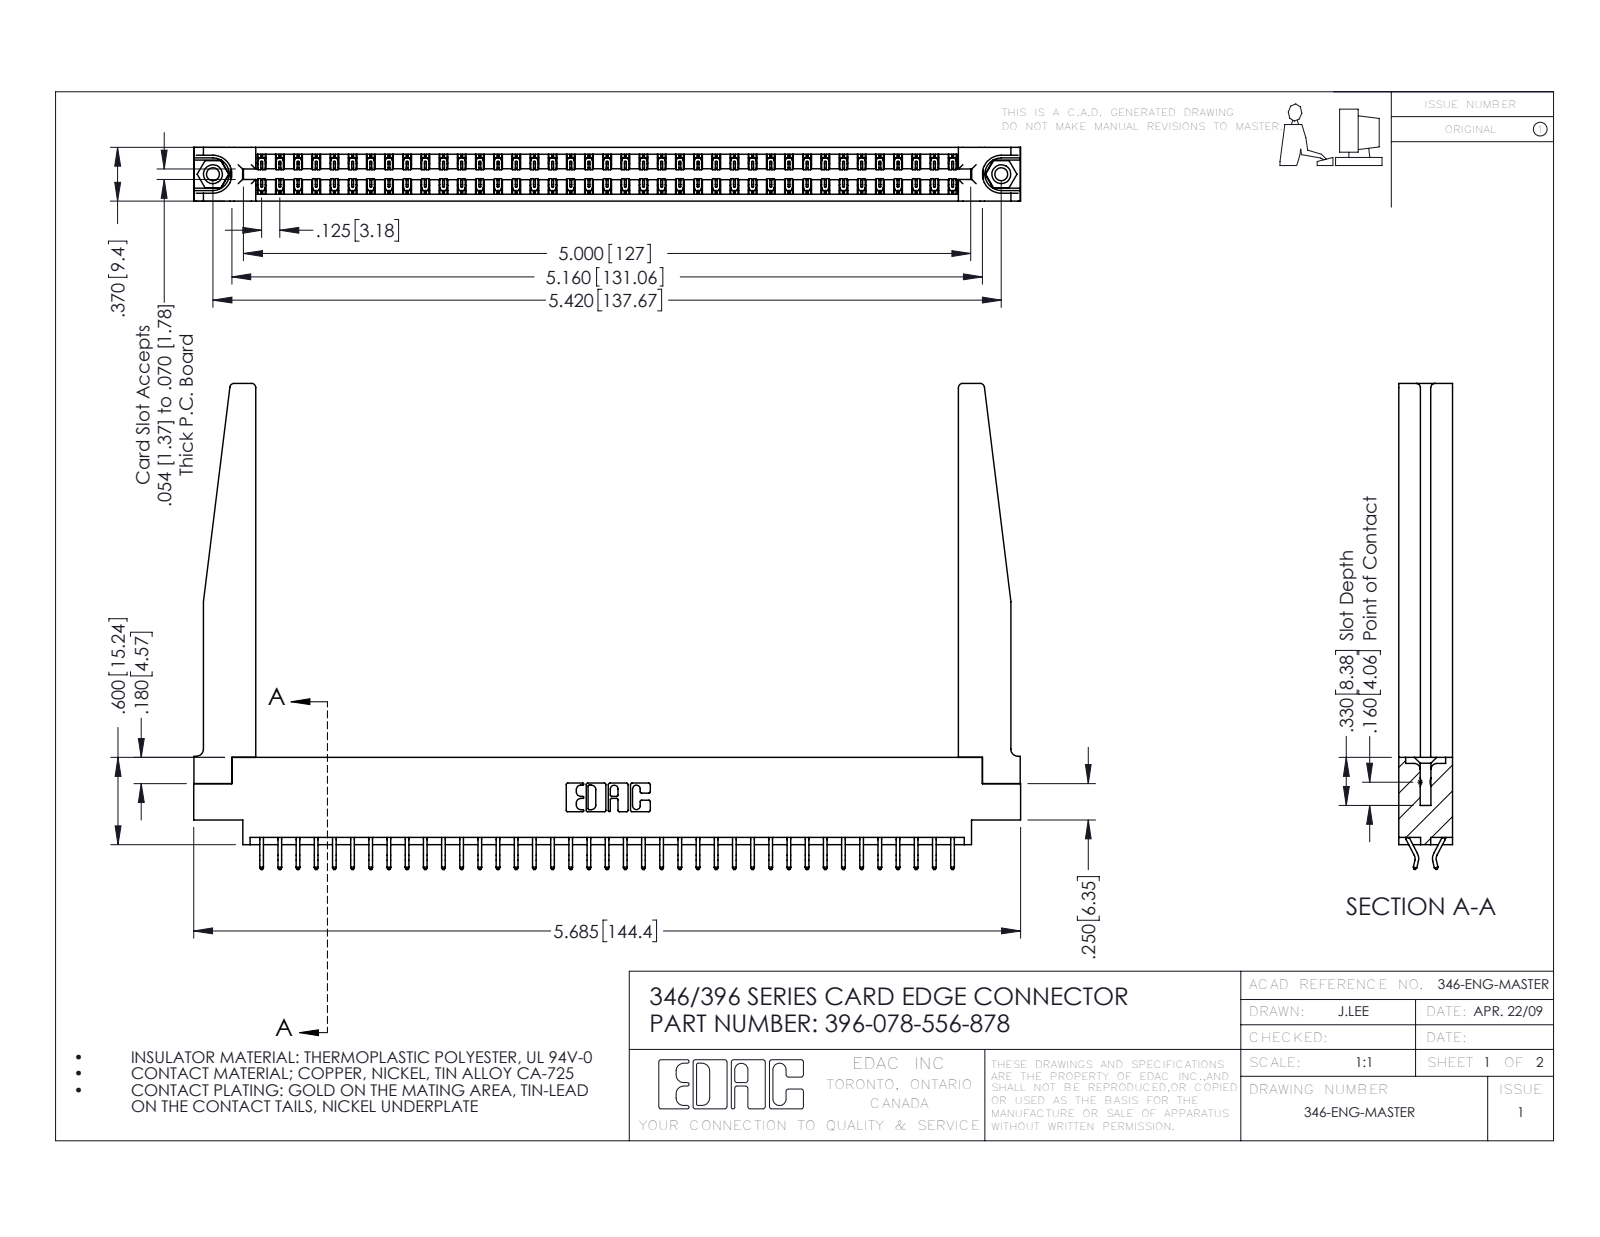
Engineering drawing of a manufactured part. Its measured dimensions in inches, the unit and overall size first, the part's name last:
Units: inches
Overall size (bounding box): 5.685 × 3.34 × 0.37
Round holes (diameter × count): ⌀0.089 ×2, ⌀0.125 ×2, ⌀0.156 ×2, ⌀0.064 ×1
Round bosses / shafts (diameter × count): ⌀0.155 ×2
Partial cylindrical surfaces — rounded edges, fillets, slot ends (radius × count): R0.006 ×117, R0.01 ×22, R0.03 ×8, R0.007 ×6, R0.031 ×6, R0.05 ×4, R0.026 ×3, R0.01 ×2
Main face-to-face distances: 0.37, 0.048, 0.322, 0.072, 0.148, 0.15, 0.25, 0.025, 0.298, 0.275
Hole centre spacings: 0.246, 5.211, 5.42
Volume: 1.27 in³ · Surface area: 39.84 in²
Bodies: 83 solids, 4884 faces (3264 planar, 1568 cylindrical, 52 other)
Part name (STEP PRODUCT): 346-220-078_345-220-078; 346 Part_0.170 Offset - 0.156 Dia-TH; 345-250-001_345-250-001-102; 396-078-556-878 (+1 more)
STEP written by: SolidWorks 2016 (CONFIG_CONTROL_DESIGN)
